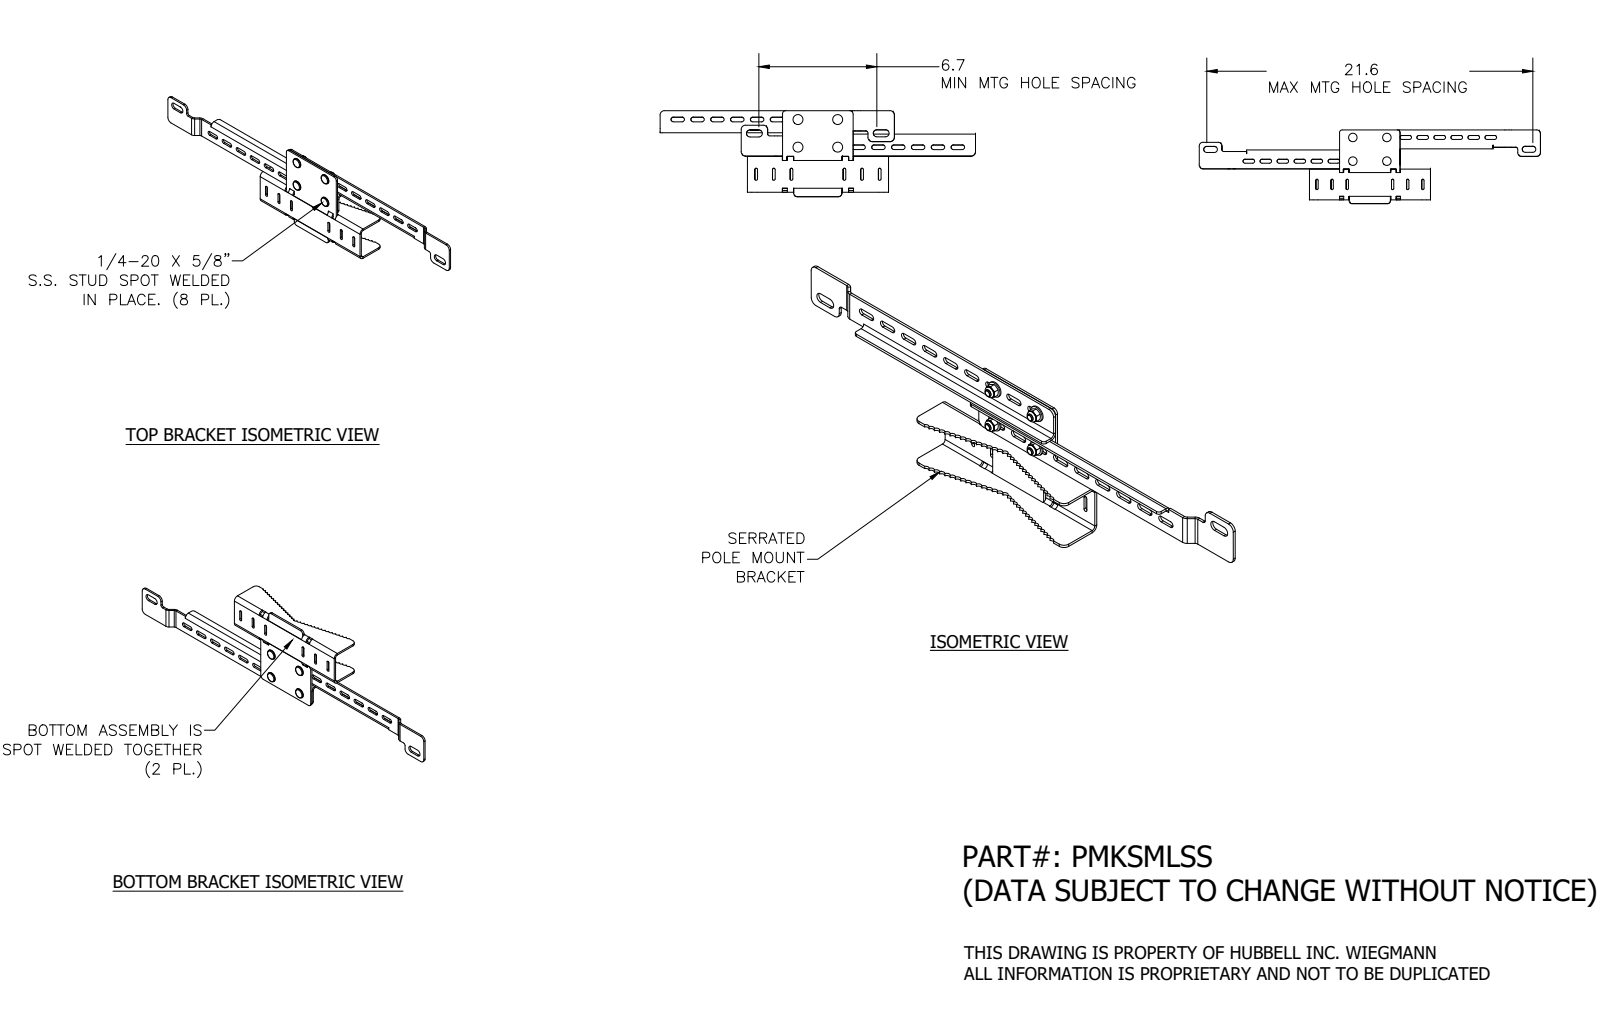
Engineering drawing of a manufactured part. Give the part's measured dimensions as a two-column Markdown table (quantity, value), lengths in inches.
| quantity | value |
| --- | --- |
| part name | PMKSMLSS |
| STEP written by | SolidWorks 2019 (AUTOMOTIVE_DESIGN) |
| units | inches |
| bodies | 26 solids, 1996 faces (576 planar, 231 cylindrical, 1189 other) |
| overall size | 22.685 × 16.666 × 4.87 |
| volume | 10.91 in³ |
| surface area | 276.7 in² |
| round holes (diameter × count) | 0.196 × 4, 0.252 × 4, 0.29 × 4, 0.307 × 2, 0.335 × 2, 0.375 × 2 |
| round bosses / shafts (diameter × count) | 0.625 × 4, 0.563 × 4, 0.25 × 4, 0.435 × 3, 1.075 × 2, 0.562 × 2, 0.375 × 2, 1.125 × 1 |
| partial cylindrical surfaces (radius × count) | 0.125 × 39, 0.13 × 36, 0.023 × 14, 0.25 × 14, 0.075 × 12, 0.141 × 8, 0.245 × 8, 0.031 × 4 |
| main face-to-face distances | 0.104, 0.105, 0.103, 0.208, 0.21, 0.106, 0.105, 0.209, 0.314, 0.209 |
| hole center spacings | 1.563, 11.93, 9.686, 9.686, 2.25, 2.739, 11.931, 2.25 |
